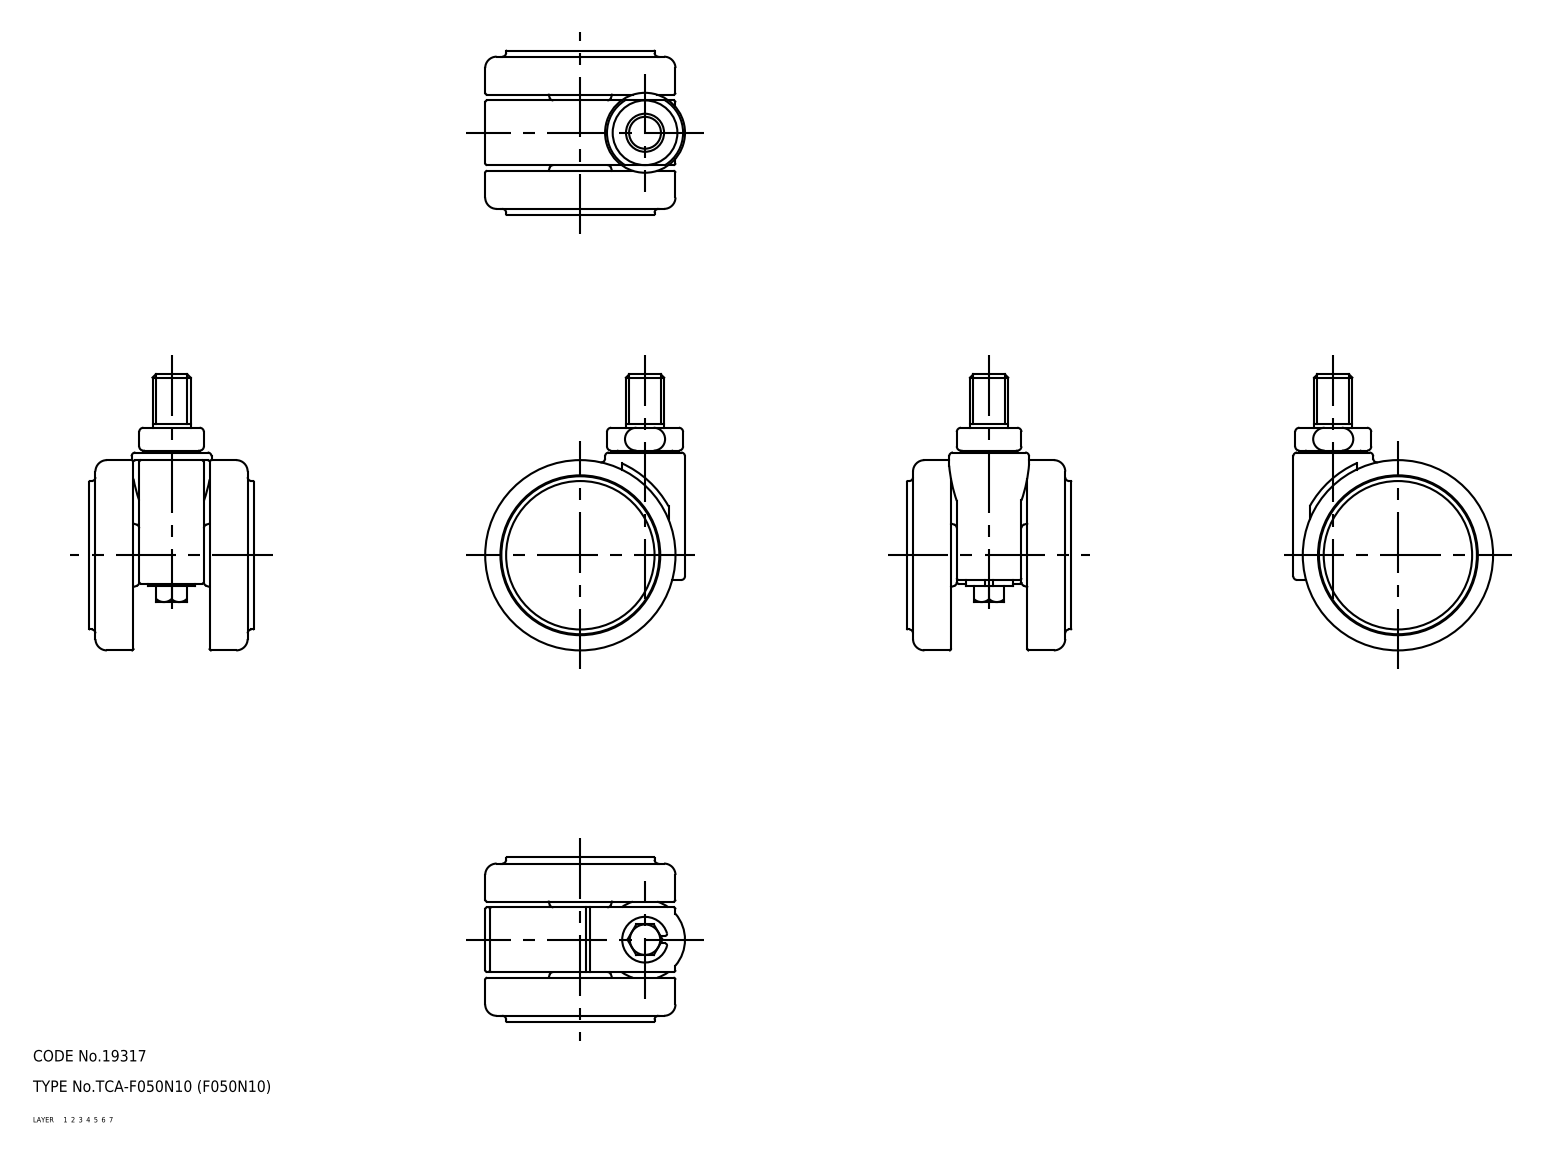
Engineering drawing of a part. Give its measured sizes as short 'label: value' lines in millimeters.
name: 67117955; 67117968; 67117981; 67117994
written by: CADfix (AUTOMOTIVE_DESIGN)
unit: mm
bodies: 4 solids, 131 faces (0 planar, 0 cylindrical, 131 other)
size: 72.5 × 52.5 × 43.2
volume: 61 543 mm³; area: 21 351 mm²
